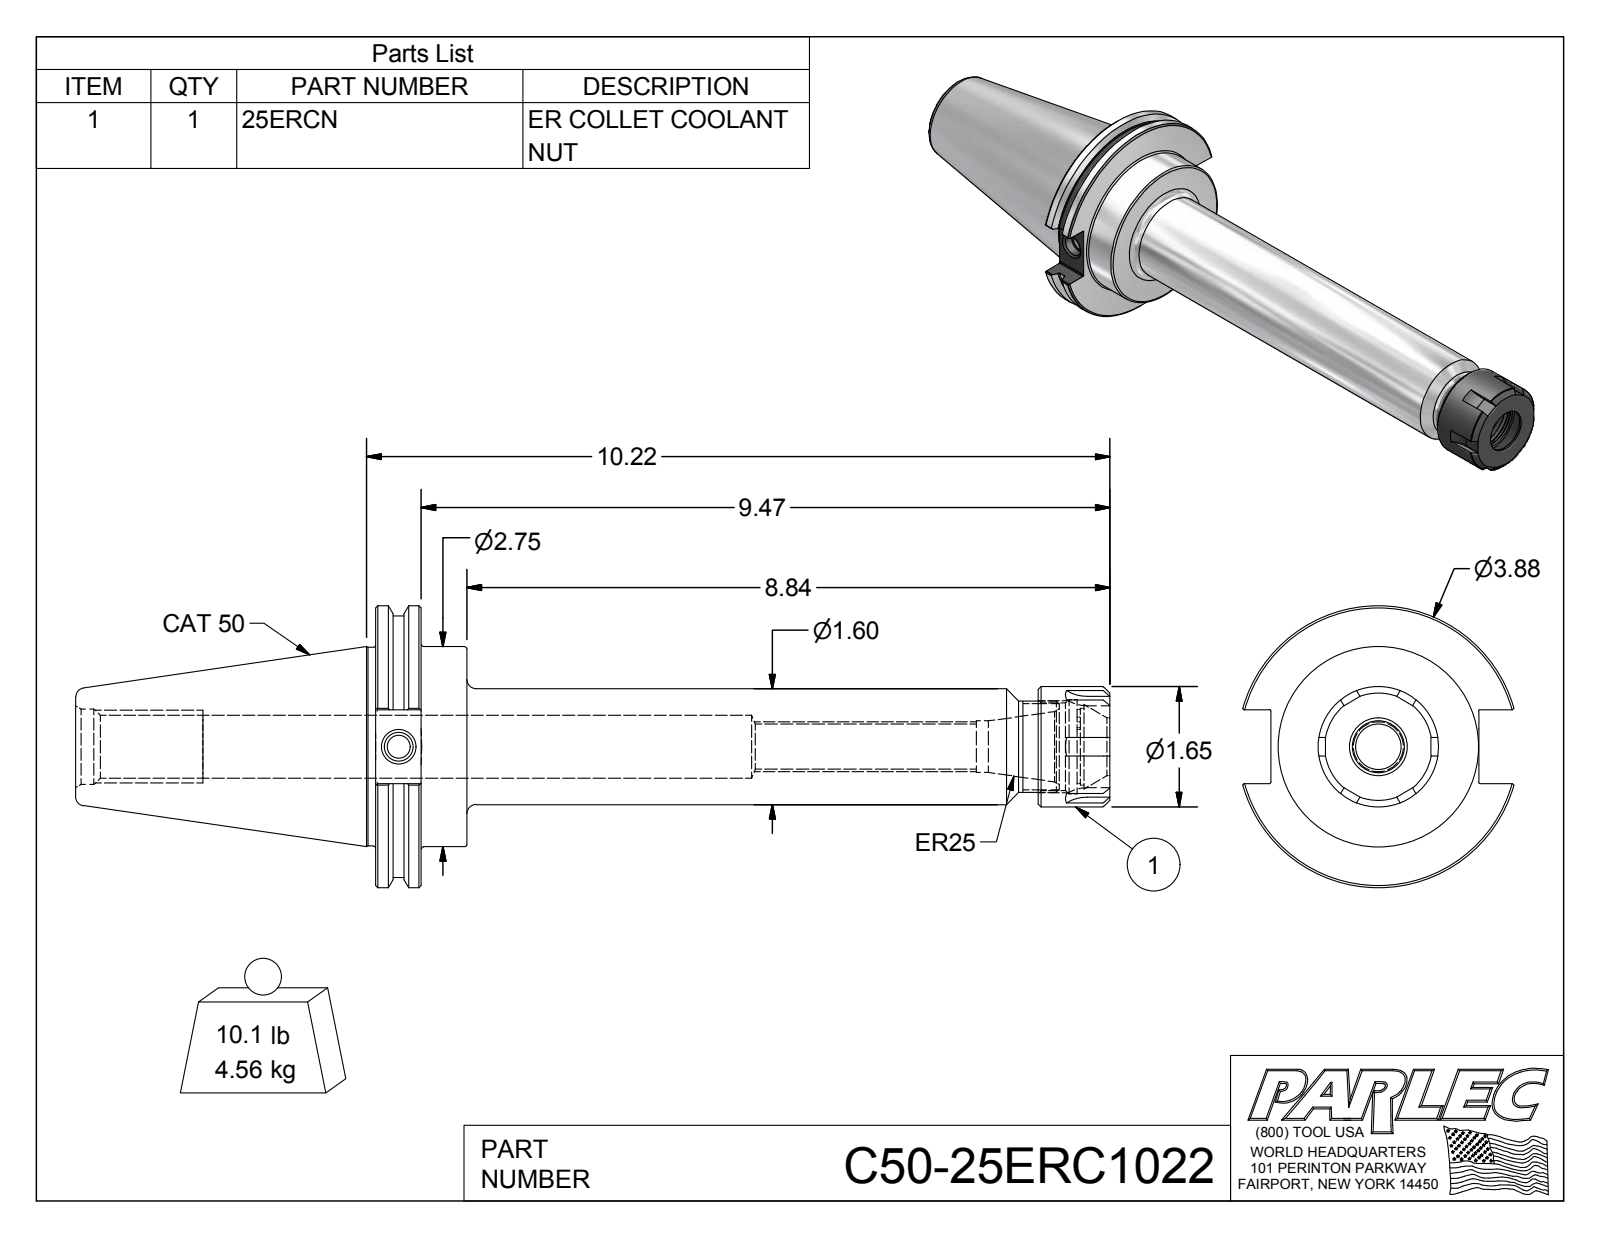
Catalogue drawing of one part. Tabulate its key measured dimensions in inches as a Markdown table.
| quantity | value |
| --- | --- |
| part name | C50-25ERC1022; C50-25ER10-1; 25ERCN |
| STEP written by | Autodesk Inventor 2012 (AUTOMOTIVE_DESIGN) |
| units | inches |
| bodies | 2 solids, 139 faces (57 planar, 41 cylindrical, 41 other) |
| overall size | 14.22 × 3.875 × 3.729 |
| volume | 35.73 in³ |
| surface area | 146.2 in² |
| round holes (diameter × count) | 0.315 × 1, 0.399 × 1, 0.62 × 1, 0.71 × 1, 0.794 × 1, 0.864 × 1, 0.865 × 1, 1.038 × 1, 1.057 × 1, 1.201 × 1, 1.294 × 1 |
| round bosses / shafts (diameter × count) | 3.875 × 1, 3.594 × 1, 2.75 × 1, 2.73 × 1, 1.654 × 1, 1.595 × 1, 1.26 × 1 |
| partial cylindrical surfaces (radius × count) | 0.02 × 8, 0.5 × 6, 0.472 × 1, 0.515 × 1 |
| main face-to-face distances | 0.625, 1.255, 0.63, 10.095, 9.47, 8.84, 9.111, 8.486, 7.856, 0.984 |
